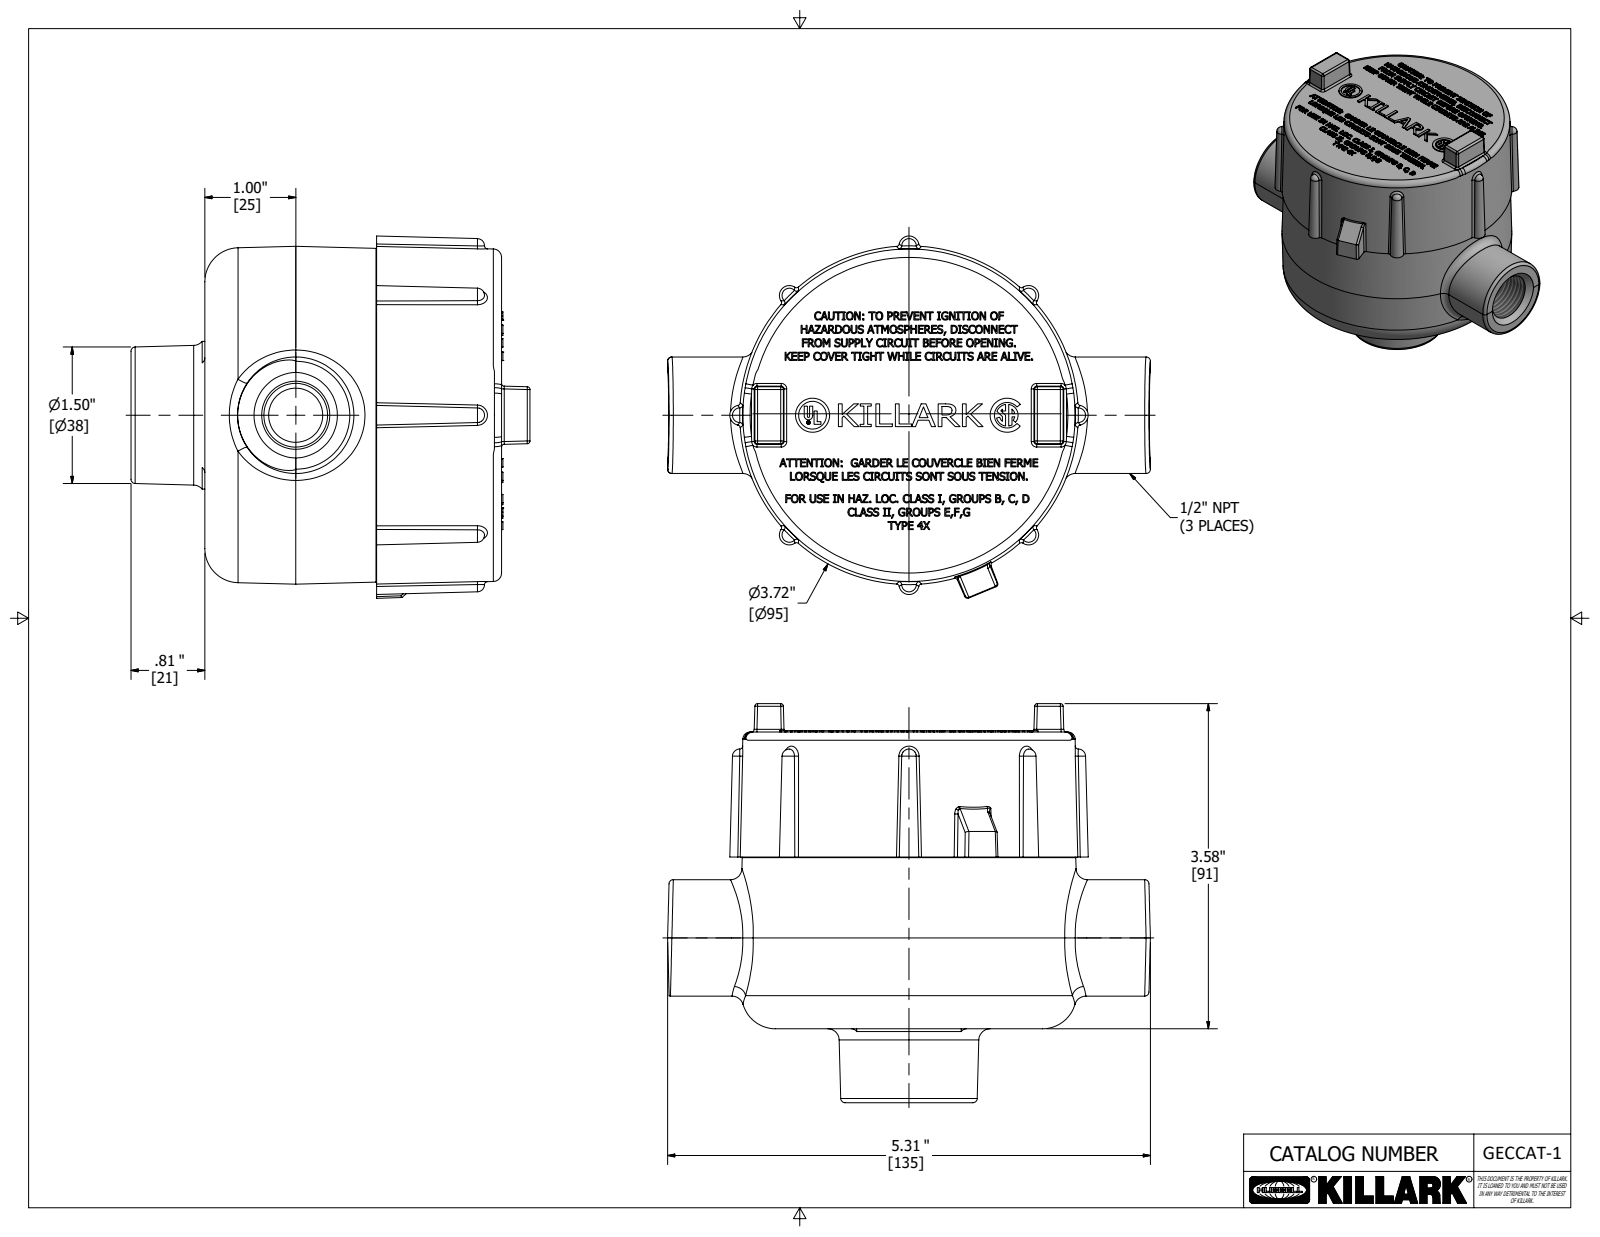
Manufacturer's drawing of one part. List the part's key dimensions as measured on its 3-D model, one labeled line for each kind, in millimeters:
Part name (STEP PRODUCT): GECCAT-1; 17061-2; 18476-1
STEP written by: Autodesk Inventor 2020 (AUTOMOTIVE_DESIGN)
Units: millimetres
Bodies: 2 solids, 4995 faces (3064 planar, 69 cylindrical, 1862 other)
Overall size (bounding box): 135.3 × 111.5 × 101.2
Volume: 299 200 mm³ · Surface area: 93 290 mm²
Round holes (diameter × count): ⌀15.1 ×2, ⌀0.9 ×1, ⌀3.7 ×1, ⌀7.8 ×1, ⌀82.6 ×1
Round bosses / shafts (diameter × count): ⌀80.9 ×1, ⌀77.7 ×1, ⌀32.5 ×1, ⌀9.5 ×1, ⌀1.1 ×1
Partial cylindrical surfaces — rounded edges, fillets, slot ends (radius × count): R0.8 ×20, R0.8 ×10, R0.1 ×1, R0.2 ×1, R0.3 ×1, R1.2 ×1, R2.2 ×1, R3 ×1
Main face-to-face distances: 8.7, 68.6, 77.4, 42.4, 26.2, 34.9, 5.6, 48, 74.2, 82.9
Hole centre spacings: 2.3, 26.9, 27, 28.2, 49.8, 51.7
